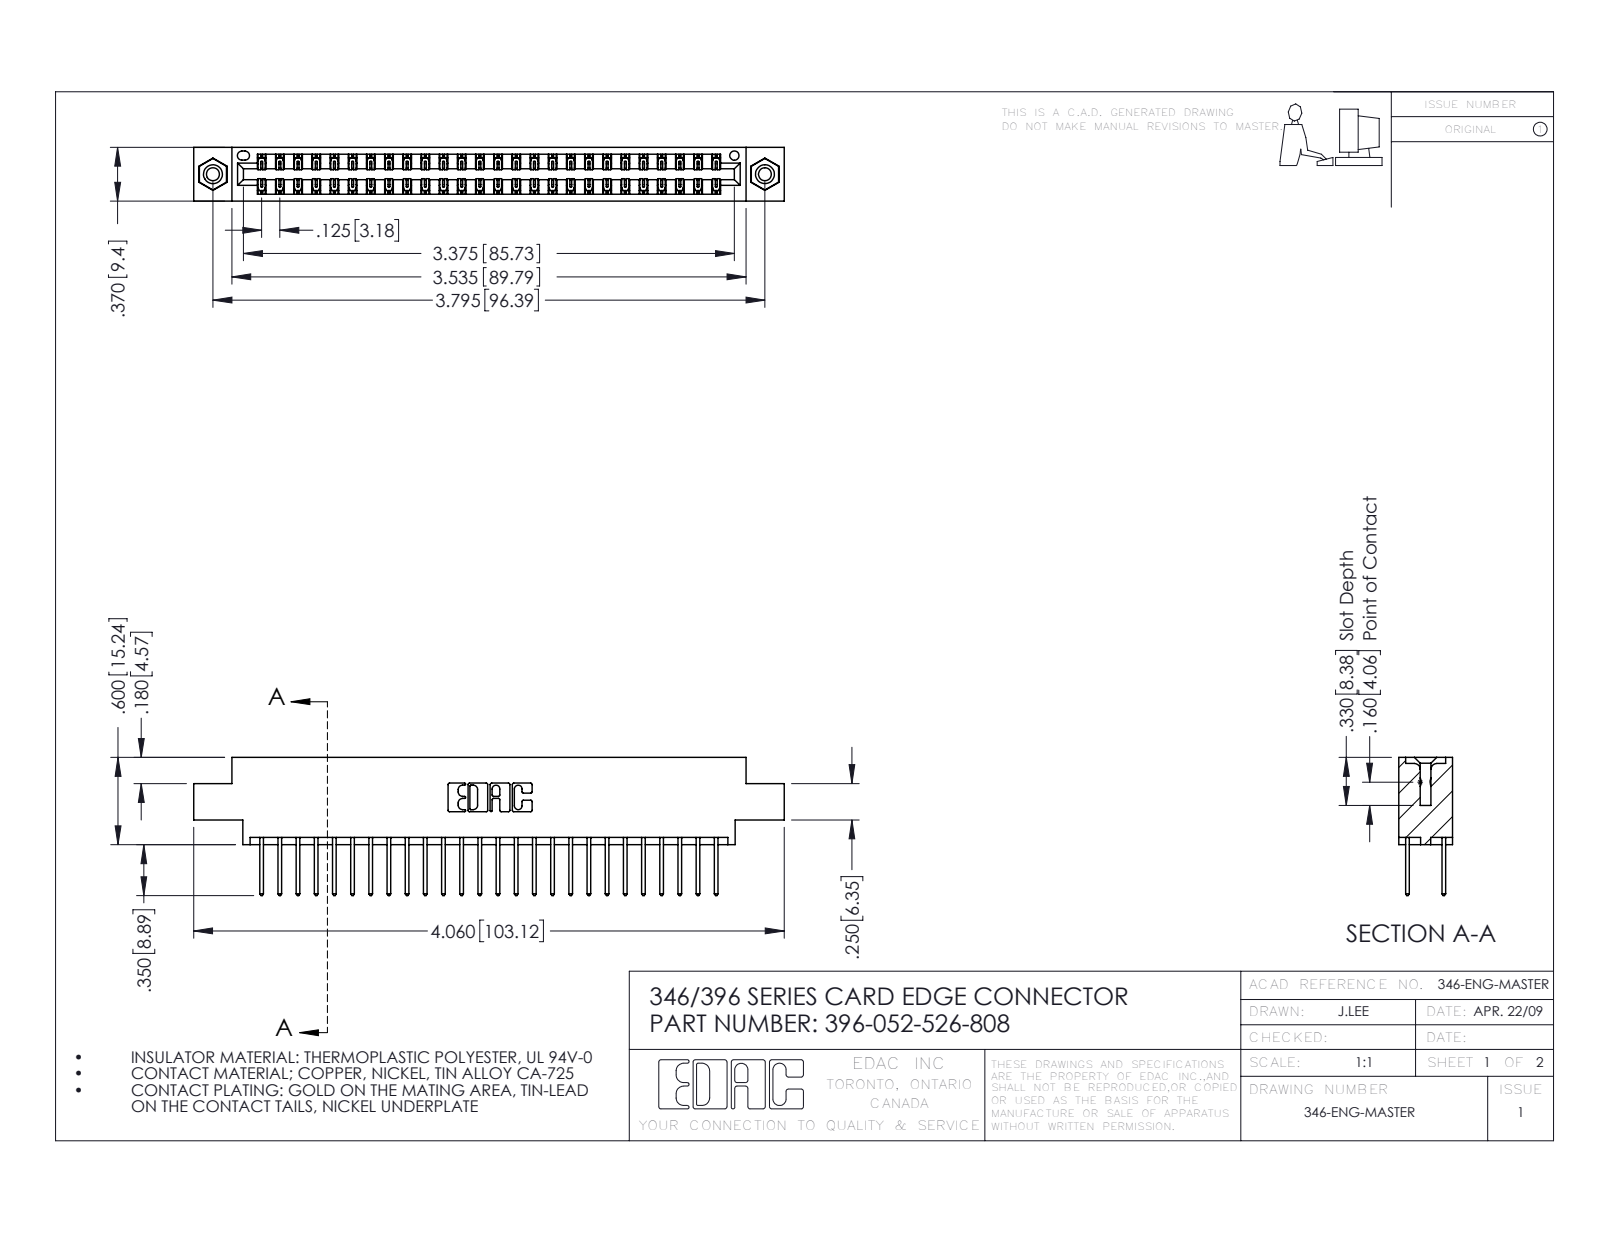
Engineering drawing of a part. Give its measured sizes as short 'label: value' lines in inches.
name: 345-292-001_345-293-126; 396-052-526-808; 346 Part_0.170 Offset - 0.156 Dia-TI; 345-250-001_345-250-003-102
written by: SolidWorks 2016 (CONFIG_CONTROL_DESIGN)
unit: in
bodies: 55 solids, 2890 faces (1932 planar, 942 cylindrical, 16 other)
size: 4.06 × 0.95 × 0.37
volume: 0.601 in³; area: 21.51 in²
holes: 2× ⌀0.089, 2× ⌀0.125, 2× ⌀0.156, 1× ⌀0.064
bosses: 2× ⌀0.155
rounds: 78× R0.006, 52× R0.01, 22× R0.01, 6× R0.007, 6× R0.031, 3× R0.026, 2× R0.014, 2× R0.022
face distances: 0.048, 0.322, 0.25, 0.37, 0.072, 0.298, 0.025, 0.275, 0.222, 0.148
hole spacings: 0.246, 3.587, 3.795
